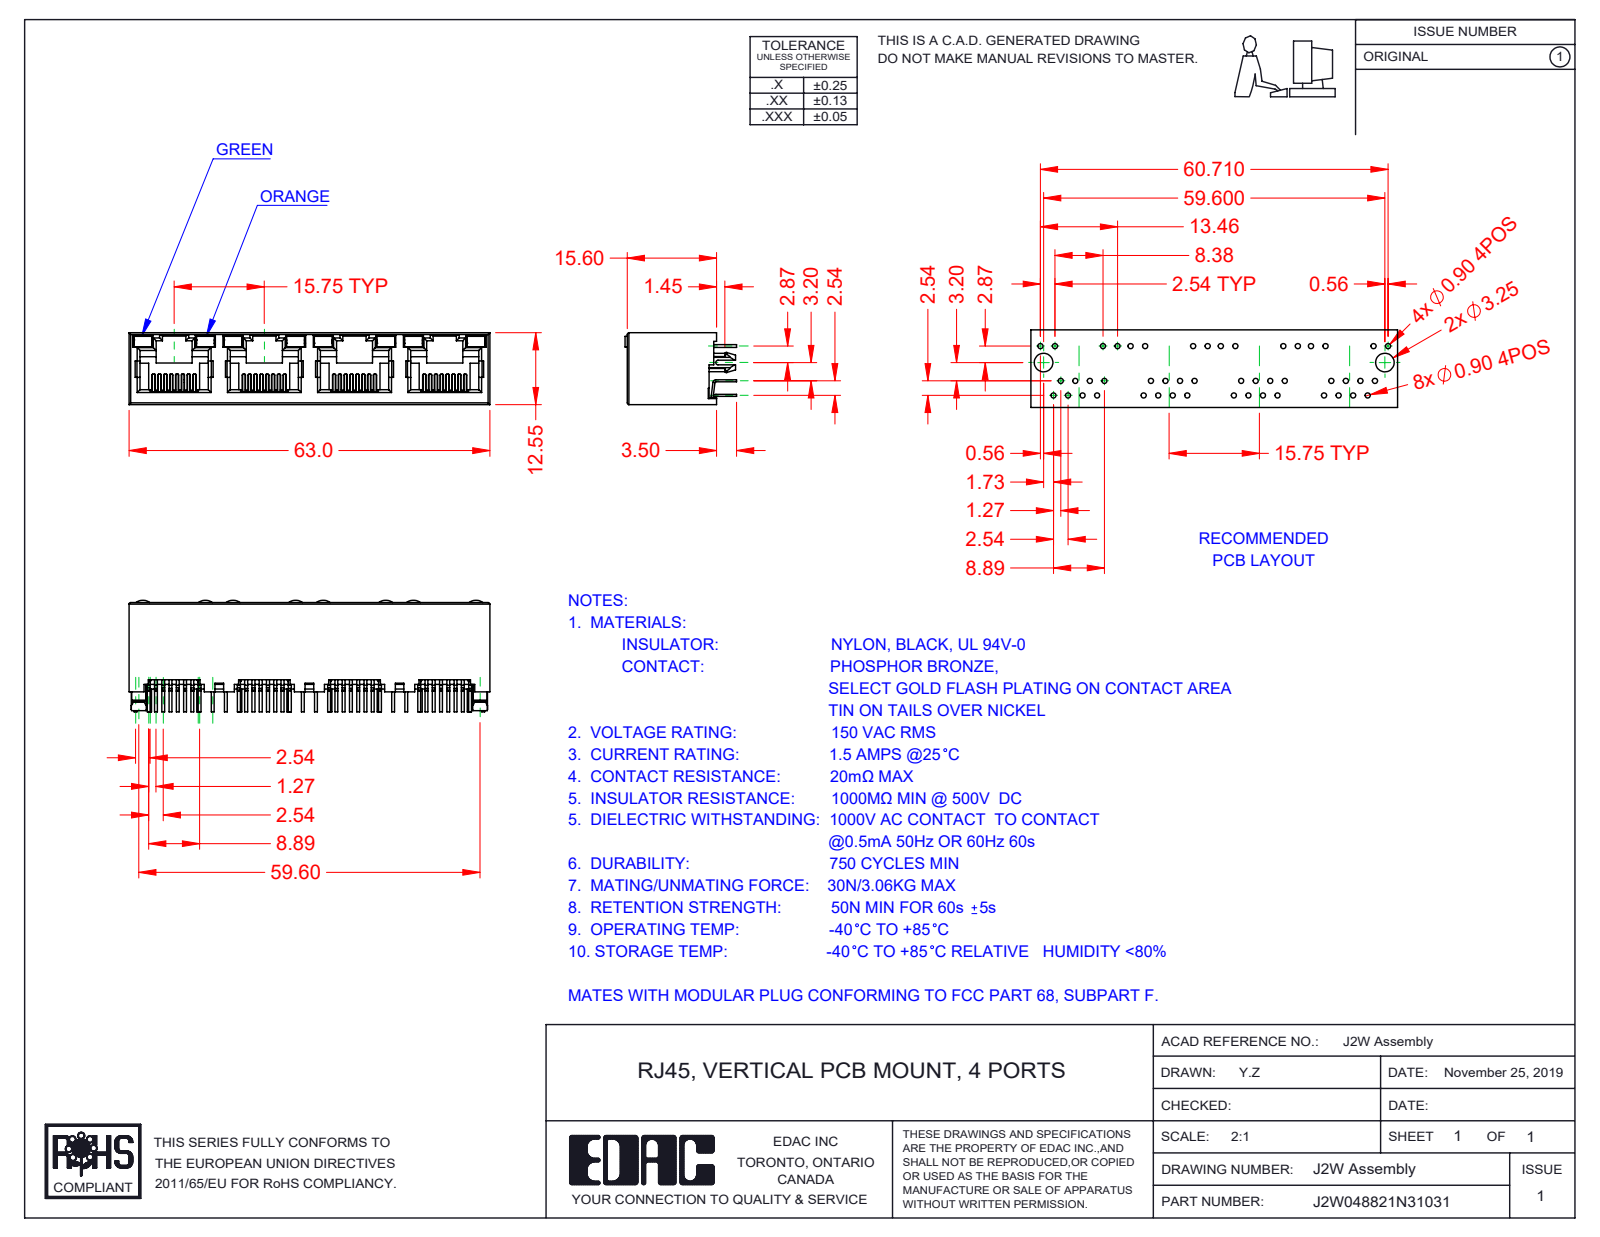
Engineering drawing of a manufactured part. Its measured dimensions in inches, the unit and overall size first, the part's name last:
Units: inches
Overall size (bounding box): 2.48 × 0.768 × 0.494
Partial cylindrical surfaces — rounded edges, fillets, slot ends (radius × count): R0.006 ×64, R0.008 ×29, R0.02 ×28, R0.012 ×14, R0.018 ×8, R0.079 ×8, R0.01 ×2, R0.059 ×2
Main face-to-face distances: 0.494, 0.469, 0.026, 0.62, 0.014, 0.059, 0.031, 0.024, 0.445, 1.24
Volume: 0.326 in³ · Surface area: 20.37 in²
Bodies: 45 solids, 3135 faces (2600 planar, 477 cylindrical, 58 other)
Part name (STEP PRODUCT): 2W Contacts; 2W Insulator; J2W048821N34131; 2W LED LH_3-Green (+2 more)
STEP written by: SolidWorks 2016 (CONFIG_CONTROL_DESIGN)
